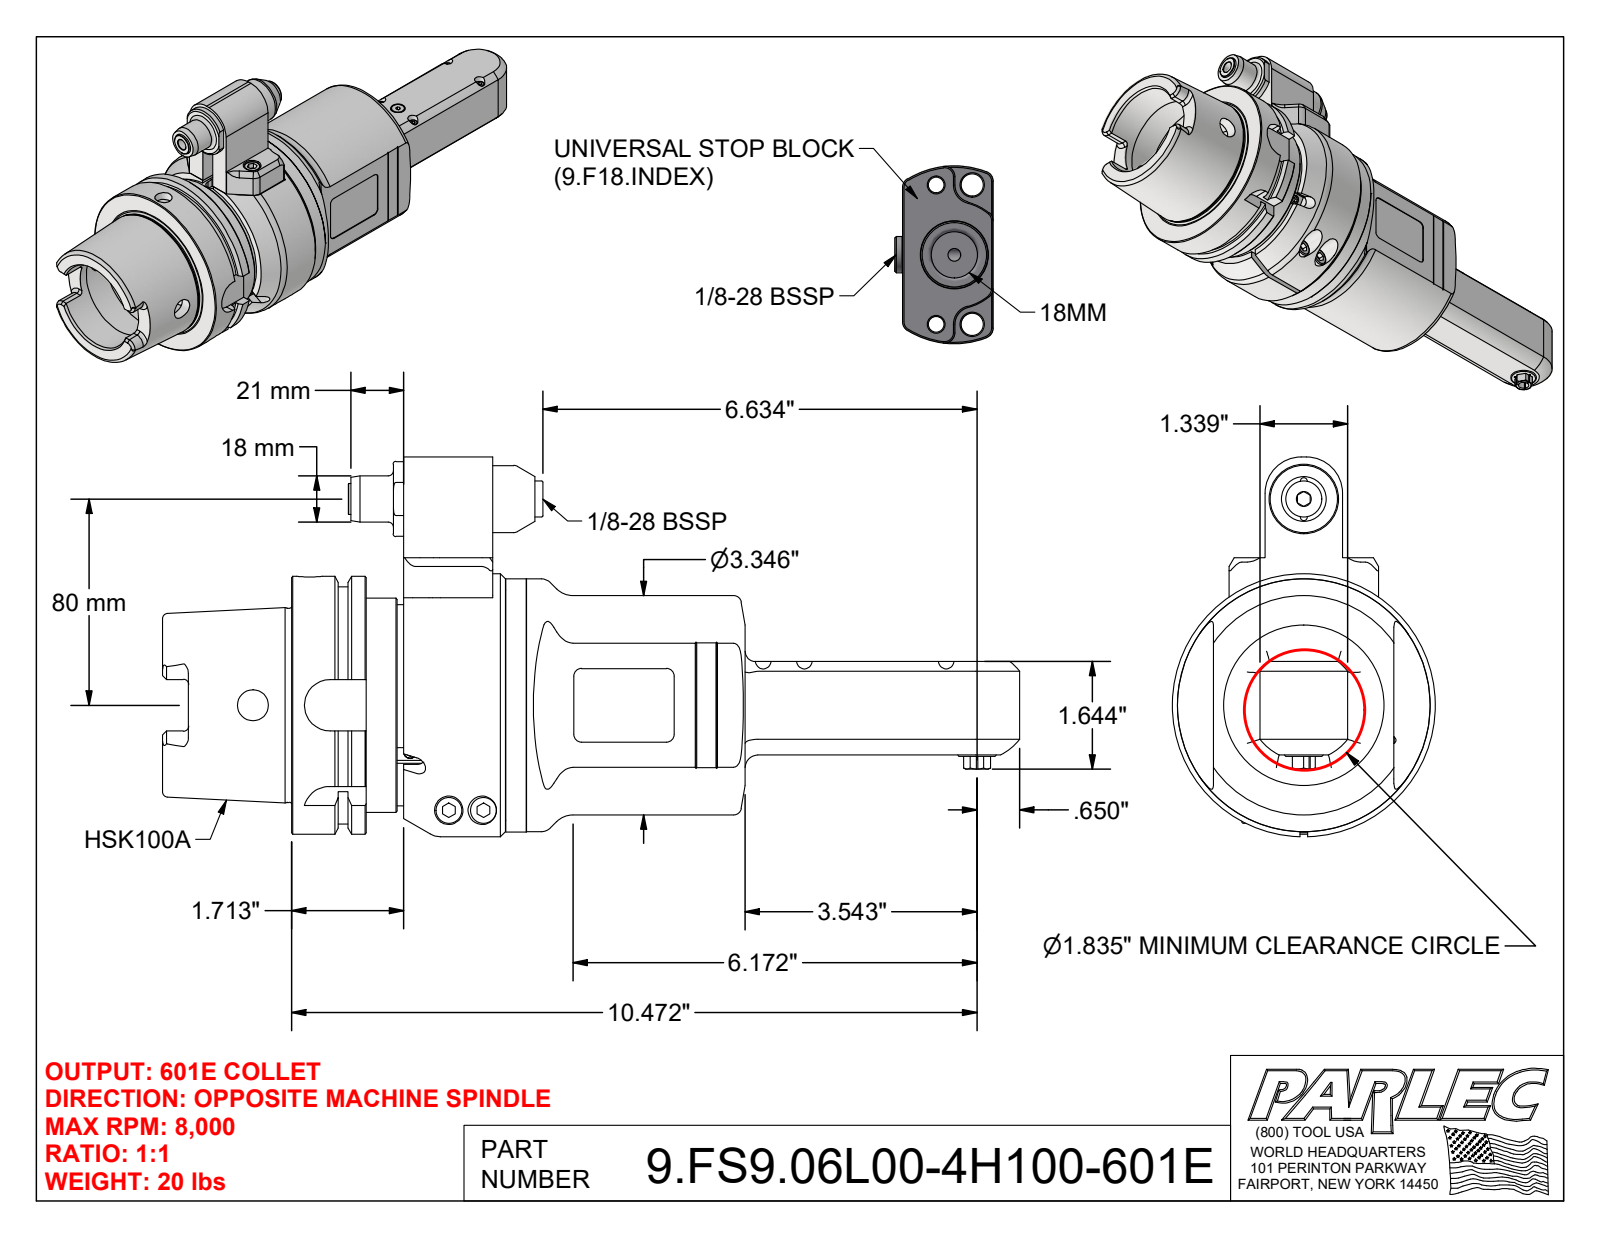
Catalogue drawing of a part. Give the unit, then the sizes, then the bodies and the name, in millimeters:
Units: millimetres
Overall size (bounding box): 332.5 × 147.2 × 102
Round holes (diameter × count): ⌀6 ×7, ⌀5 ×5, ⌀2.6 ×2, ⌀8.5 ×2, ⌀10.4 ×2, ⌀11 ×2, ⌀12 ×2, ⌀2.5 ×1, ⌀3 ×1, ⌀6.5 ×1, ⌀7 ×1, ⌀10 ×1
Round bosses / shafts (diameter × count): ⌀5.5 ×6, ⌀10 ×4, ⌀6 ×4, ⌀8 ×3, ⌀18 ×2, ⌀2.5 ×2, ⌀102 ×1, ⌀100 ×1
Partial cylindrical surfaces — rounded edges, fillets, slot ends (radius × count): R2 ×14, R4 ×6, R5 ×5, R3 ×4, R4.9 ×4, R10 ×4, R0.5 ×2, R1 ×2
Main face-to-face distances: 32, 52, 31, 18, 39.5, 1, 29, 16.5, 27, 83
Hole centre spacings: 26.5, 7, 13.3, 16, 17.9, 21.5, 31, 55
Volume: 1 336 000 mm³ · Surface area: 171 400 mm²
Bodies: 5 solids, 582 faces (305 planar, 143 cylindrical, 134 other)
Part name (STEP PRODUCT): 9.FS9.06L00-4H100-601E; 9_GA1_518_2 (Type 1, H100A, 80mm); 9_FS9_06L00_601E
STEP written by: Autodesk Inventor 2022 (AUTOMOTIVE_DESIGN)
